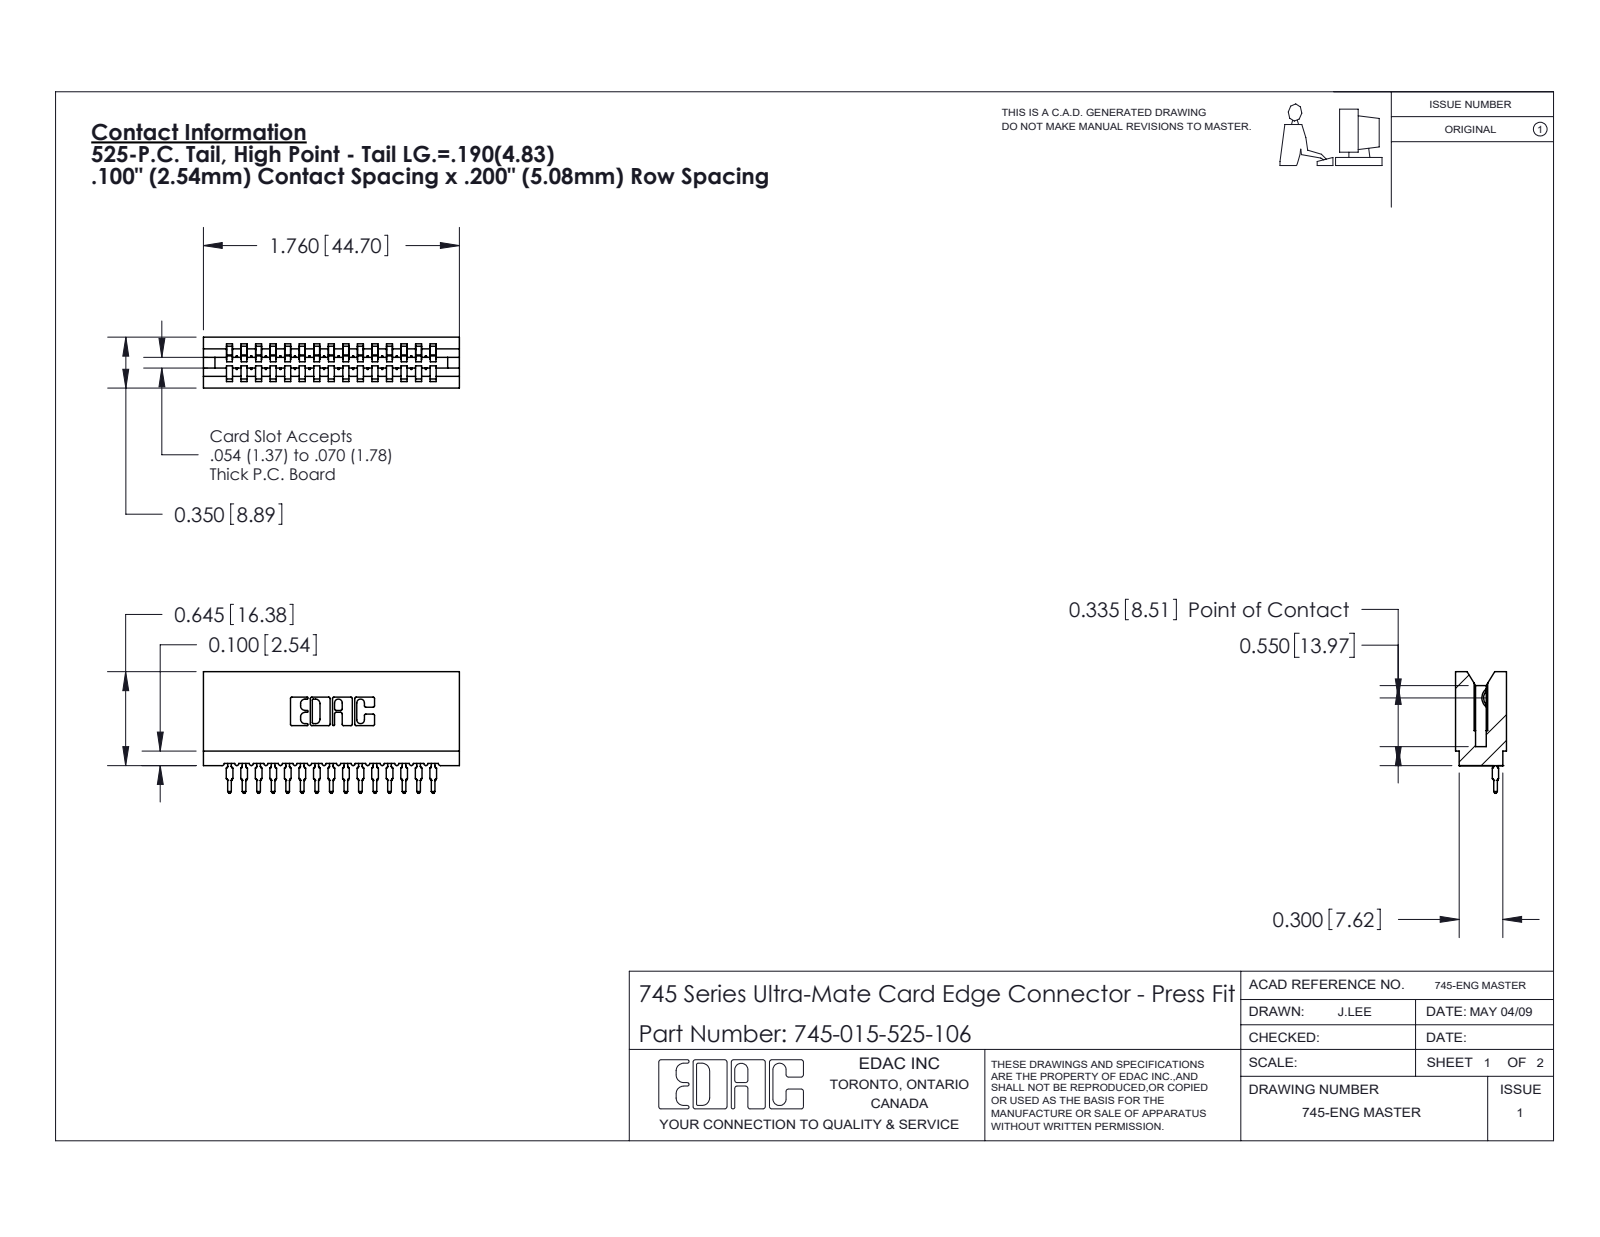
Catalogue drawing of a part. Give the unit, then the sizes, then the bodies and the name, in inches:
Units: inches
Overall size (bounding box): 1.76 × 0.836 × 0.35
Partial cylindrical surfaces — rounded edges, fillets, slot ends (radius × count): R0.015 ×30, R0.021 ×30, R0.01 ×22, R0.007 ×6, R0.031 ×6, R0.005 ×4, R0.011 ×4, R0.026 ×3
Main face-to-face distances: 0.1, 0.2, 0.3, 0.4, 0.35, 0.5, 0.6, 0.7, 0.138, 0.212
Volume: 0.245 in³ · Surface area: 10.76 in²
Bodies: 16 solids, 1776 faces (1061 planar, 325 cylindrical, 390 other)
Part name (STEP PRODUCT): 745 Part_Insulator Option - 06; 745-015-525-106; 745-292-001_525
STEP written by: SolidWorks 2020 (CONFIG_CONTROL_DESIGN)
